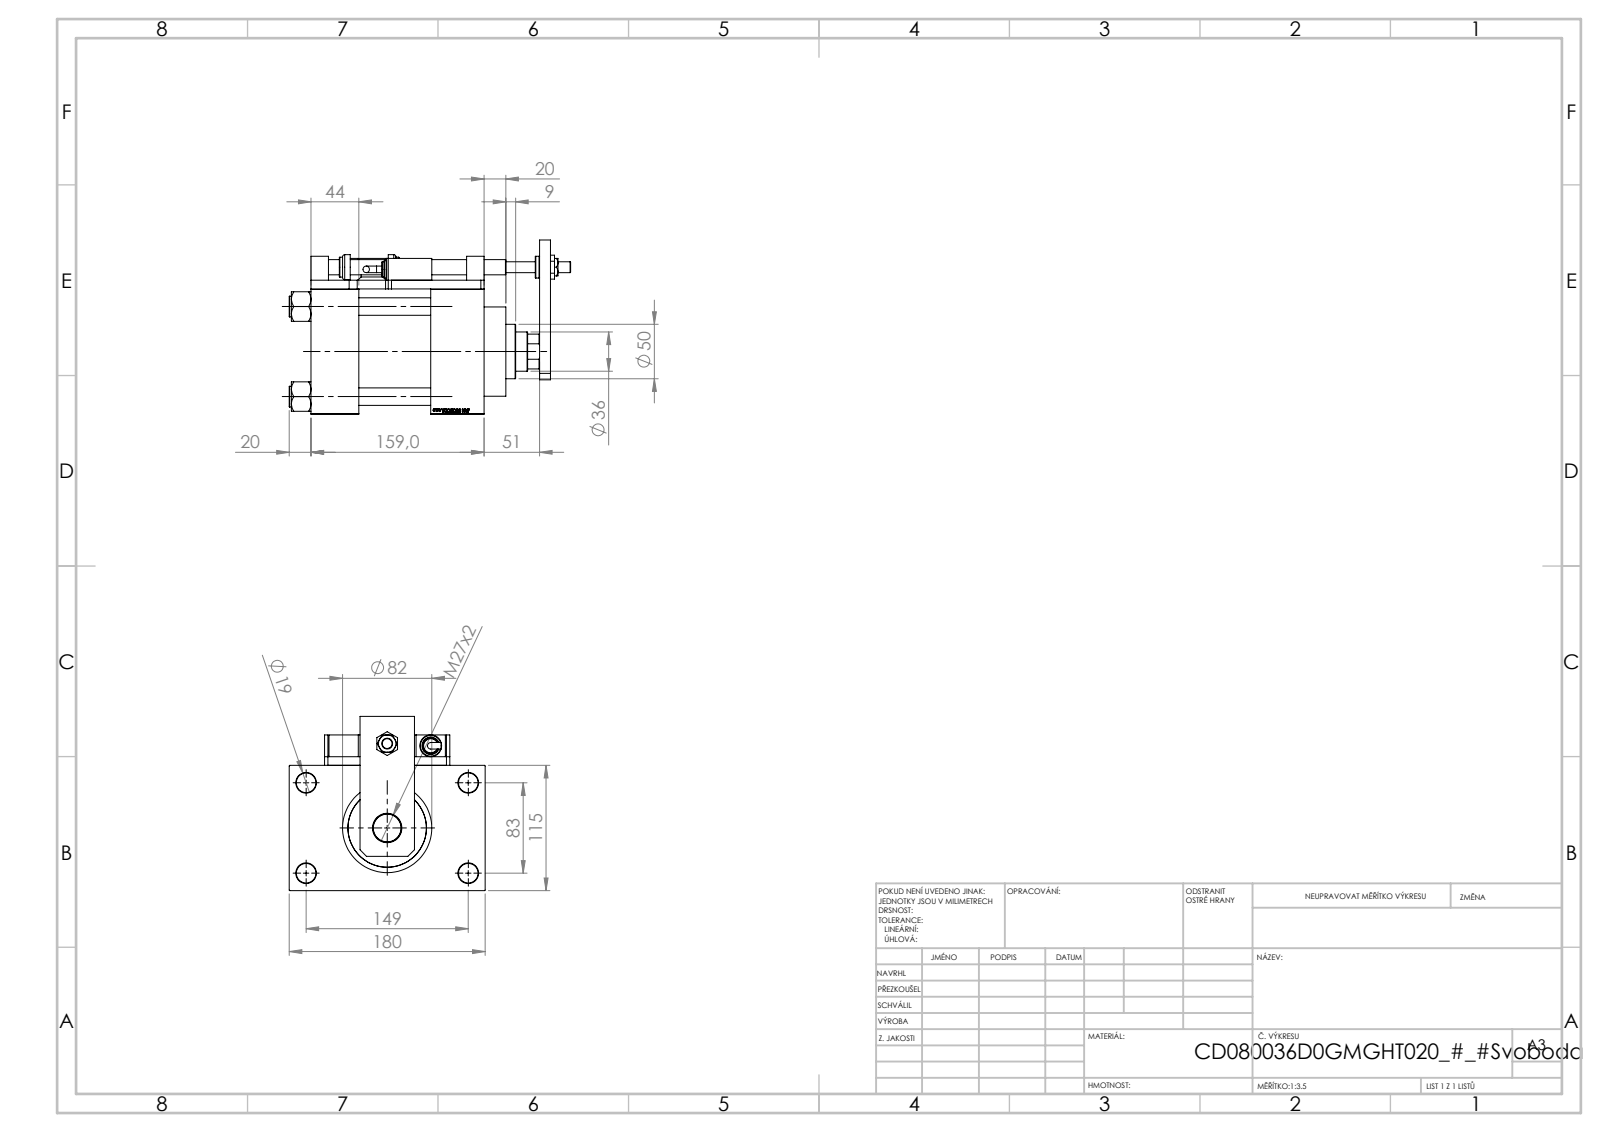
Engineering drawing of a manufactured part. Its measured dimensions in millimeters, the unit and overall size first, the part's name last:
Units: millimetres
Overall size (bounding box): 258.5 × 180 × 160
Round holes (diameter × count): ⌀8.5 ×4, ⌀13.5 ×4, ⌀16 ×4, ⌀18 ×4, ⌀7 ×2, ⌀26.44 ×2, ⌀35 ×2, ⌀10 ×1, ⌀14 ×1, ⌀25.5 ×1, ⌀27 ×1, ⌀36 ×1
Round bosses / shafts (diameter × count): ⌀19 ×4, ⌀20 ×3, ⌀16 ×2, ⌀14 ×2, ⌀6 ×2, ⌀86 ×1, ⌀82 ×1, ⌀50 ×1
Partial cylindrical surfaces — rounded edges, fillets, slot ends (radius × count): R7.5 ×4, R17.5 ×1
Main face-to-face distances: 115, 110, 8, 66, 49, 123, 44, 159, 32.5, 20
Hole centre spacings: 33.15, 58.48, 82.7, 85.28, 89.24, 115.85, 142.43, 32
Volume: 2 274 000 mm³ · Surface area: 387 680 mm²
Bodies: 24 solids, 1379 faces (666 planar, 156 cylindrical, 557 other)
Part name (STEP PRODUCT): V215CD_SWITCH_Q_ZARAZKA; V215CD_SWITCH_Q_PODLOZKA_FRONT; V215CD_NUT_M5_D; V215CD_SWITCH_Q_SWITCH (+7 more)
STEP written by: SolidWorks 2019 (CONFIG_CONTROL_DESIGN)
